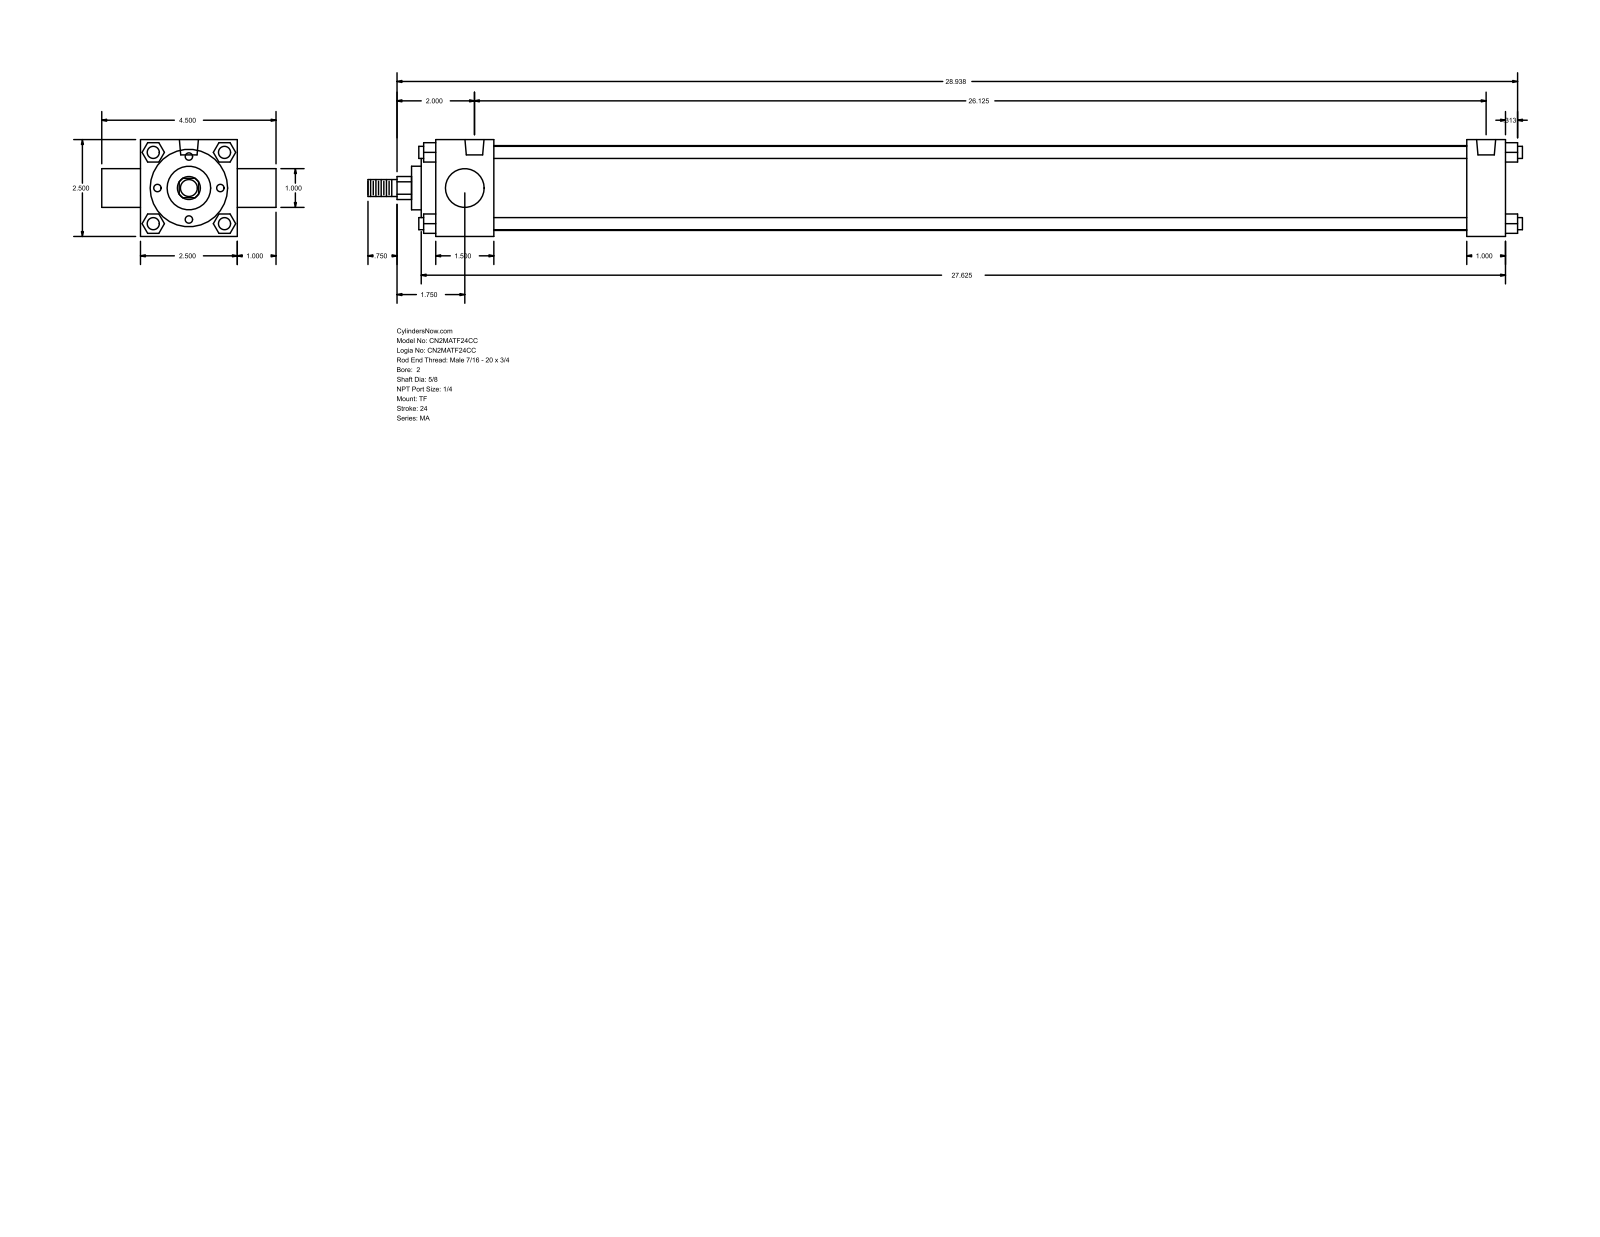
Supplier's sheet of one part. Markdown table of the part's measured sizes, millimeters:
| quantity | value |
| --- | --- |
| part name | MA_TF__0200_0.625 |
| STEP written by | GSSL Pune (CONFIG_CONTROL_DESIGN) |
| units | millimeters |
| bodies | 0 solids, 122 faces (93 planar, 29 cylindrical, 0 other) |
| overall size | 757.24 × 114.3 × 63.5 |
| round holes (diameter × count) | 7.94 × 3, 12.49 × 2 |
| round bosses / shafts (diameter × count) | 7.94 × 4, 55.63 × 1, 50.8 × 1, 28.57 × 1, 25.4 × 1, 15.88 × 1, 11.11 × 1 |
| partial cylindrical surfaces (radius × count) | 7.54 × 1 |
| main face-to-face distances | 63.5, 38.1, 12.7, 701.68, 676.27, 638.17, 663.58, 25.41, 9.52, 47.62 |
| hole center spacings | 663.58 |
